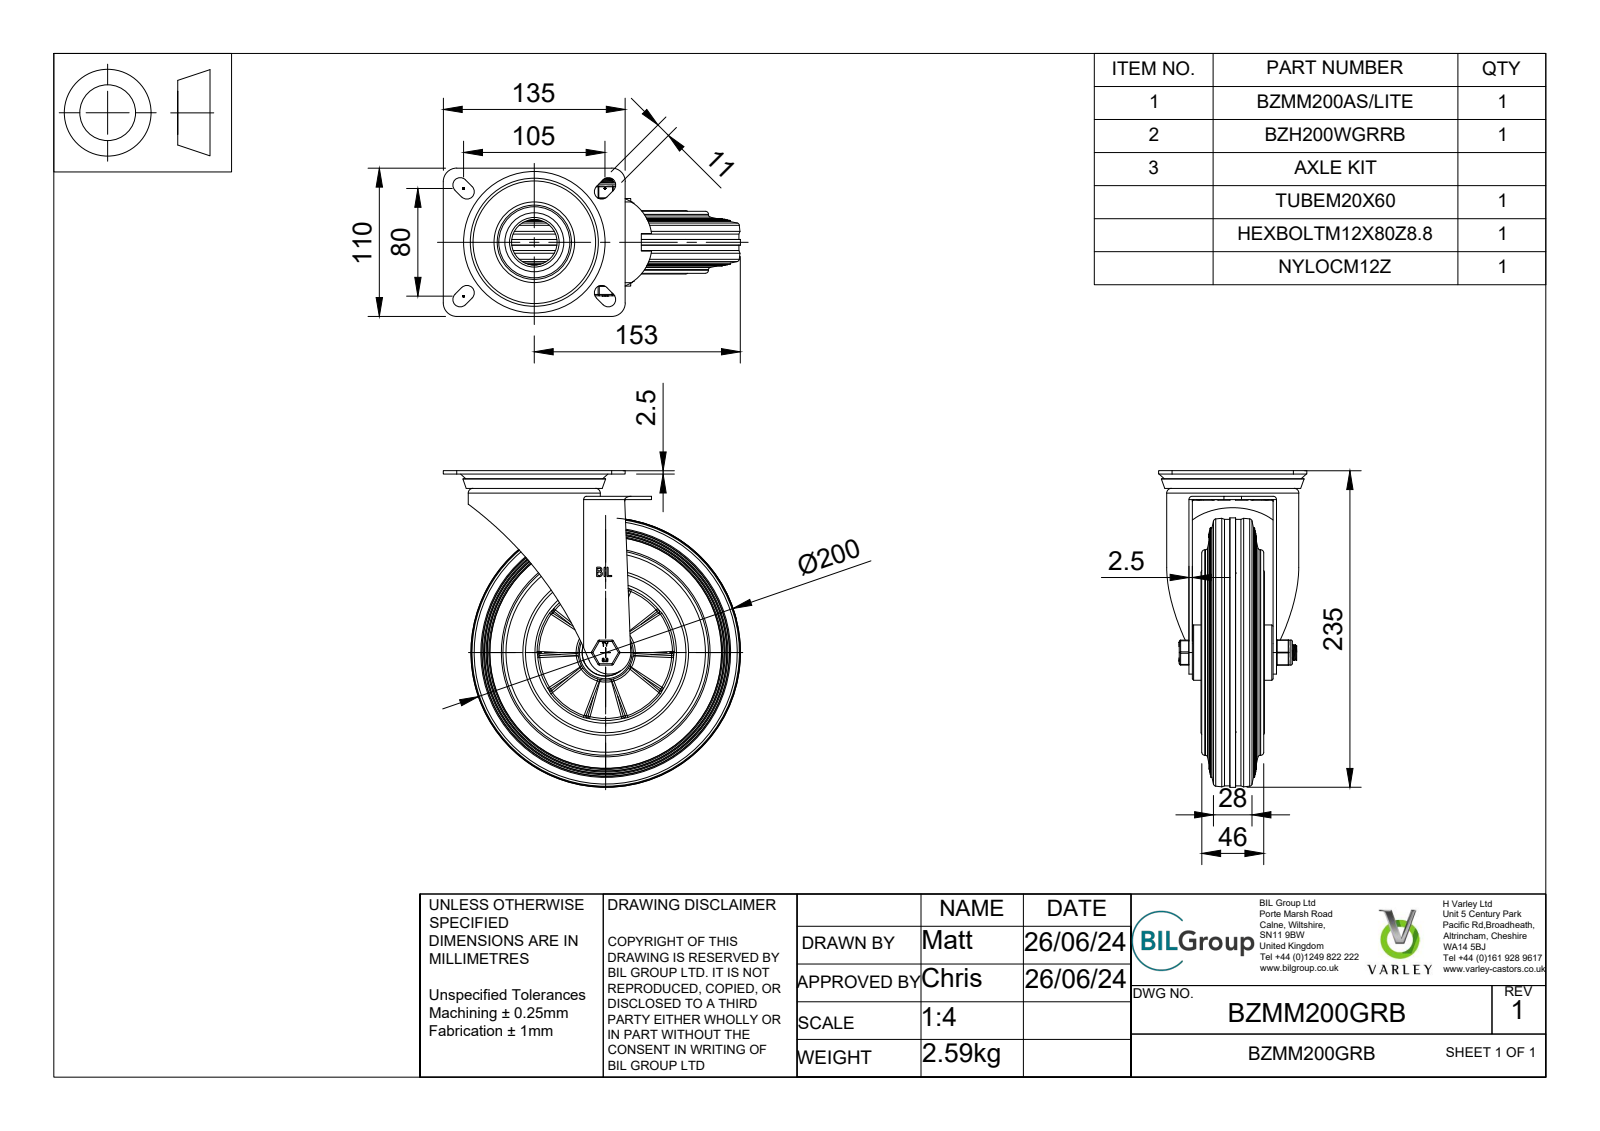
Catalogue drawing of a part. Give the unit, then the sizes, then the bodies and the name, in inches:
Units: inches
Overall size (bounding box): 9.252 × 8.681 × 4.331
Round holes (diameter × count): ⌀0.472 ×1, ⌀0.48 ×1, ⌀0.492 ×1, ⌀0.551 ×1, ⌀0.787 ×1, ⌀1.329 ×1, ⌀1.378 ×1, ⌀2.165 ×1, ⌀3.583 ×1, ⌀3.976 ×1, ⌀4.646 ×1
Round bosses / shafts (diameter × count): ⌀0.295 ×8, ⌀7.788 ×1, ⌀6.004 ×1, ⌀4.843 ×1, ⌀3.858 ×1, ⌀3.071 ×1, ⌀1.969 ×1, ⌀1.614 ×1
Partial cylindrical surfaces — rounded edges, fillets, slot ends (radius × count): R0.02 ×18, R0.039 ×12, R0.217 ×8, R0.049 ×4, R0.394 ×4, R0.098 ×2, R1.294 ×2, R0.01 ×1
Main face-to-face distances: 0.098, 0.354, 0.256, 2.106, 2.461, 0.197, 2.362, 0.531, 0.433, 0.118
Volume: 71.34 in³ · Surface area: 482 in²
Bodies: 59 solids, 875 faces (253 planar, 170 cylindrical, 452 other)
Part name (STEP PRODUCT): BZMM200GRB v3; BZMM200AS/LITE - 2 v1; ZINC PLATED, PRESSED STEEL TOP PLATE; ZINC PLATED, PRESSED STEEL TOP PLATE Geometry (+7 more)
STEP written by: Autodesk Translation Framework v13.14.0.145 (AUTOMOTIVE_DESIGN)
